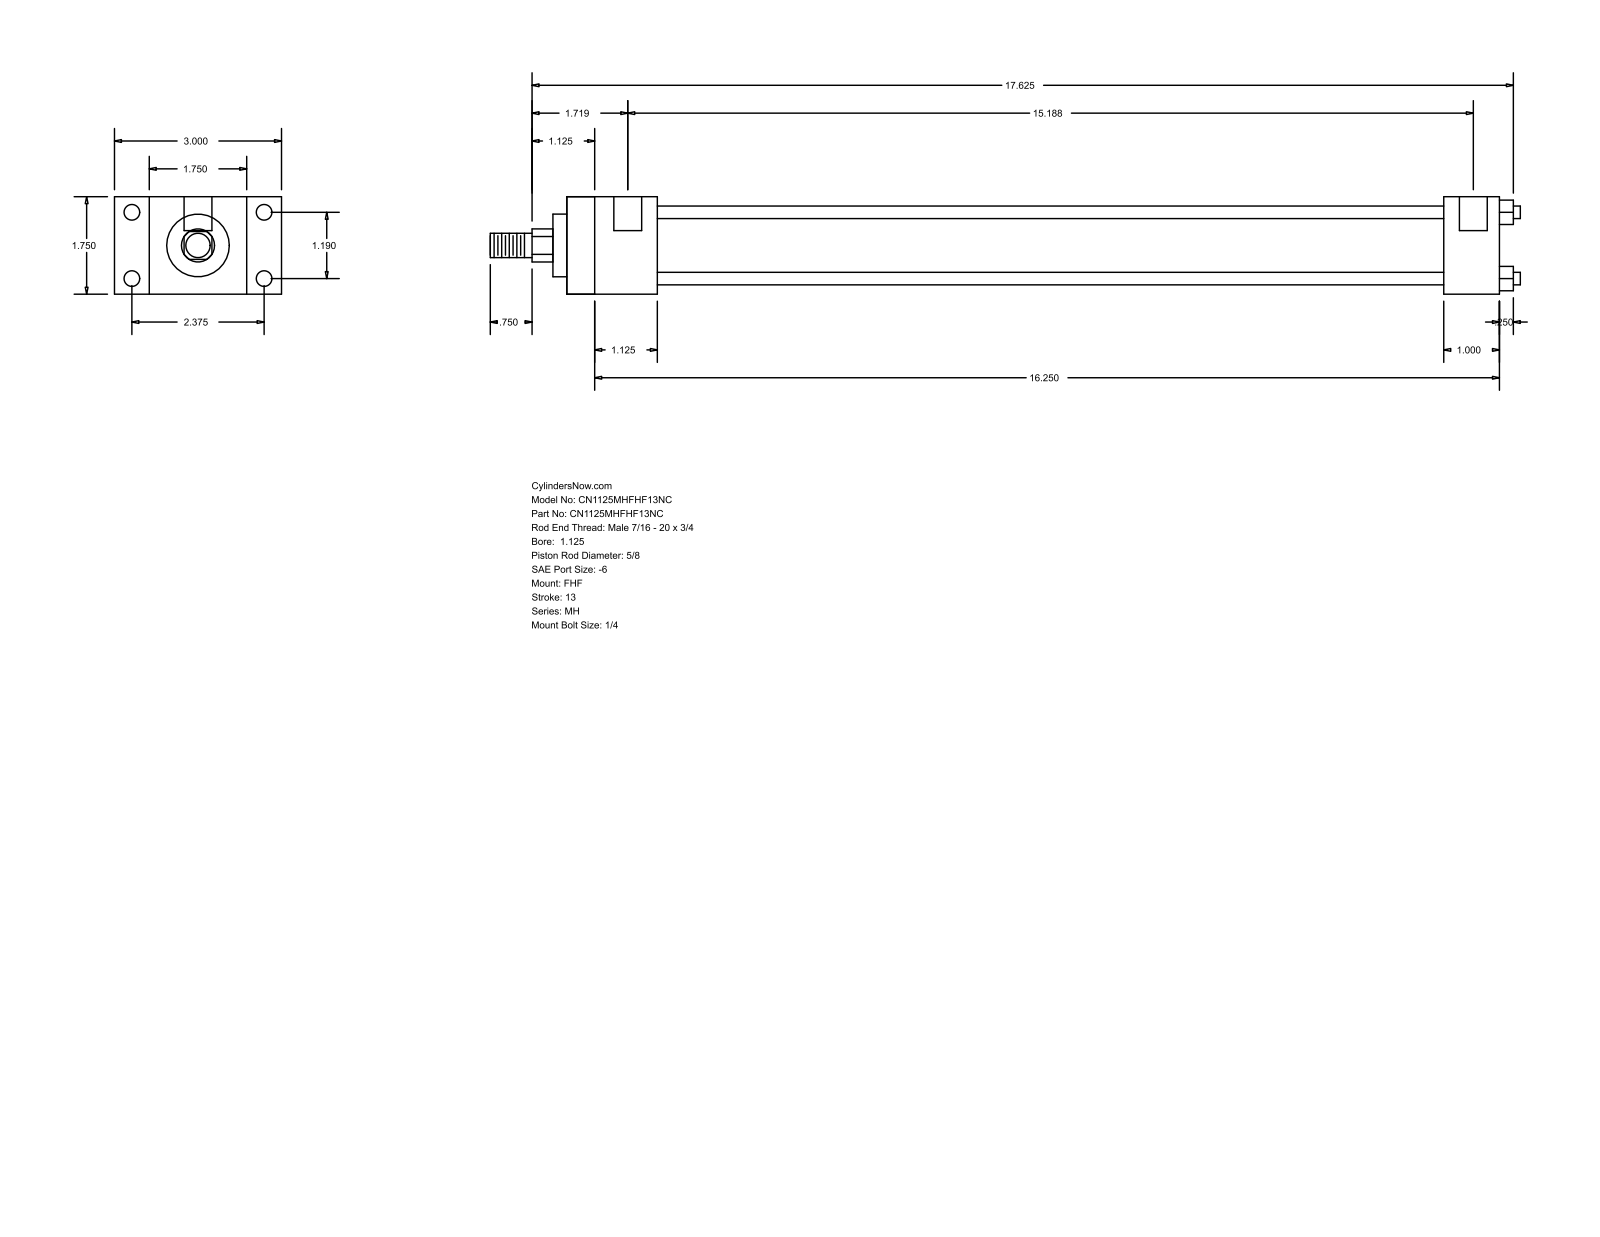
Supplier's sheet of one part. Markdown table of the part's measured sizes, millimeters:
| quantity | value |
| --- | --- |
| part name | MH_FHF__0112_0.625 |
| STEP written by | GSSL Pune (CONFIG_CONTROL_DESIGN) |
| units | millimeters |
| bodies | 0 solids, 88 faces (60 planar, 28 cylindrical, 0 other) |
| overall size | 469.9 × 76.2 × 44.45 |
| round holes (diameter × count) | 5.56 × 4, 7.14 × 4, 12.7 × 2 |
| round bosses / shafts (diameter × count) | 5.71 × 4, 34.92 × 1, 28.57 × 1, 15.88 × 1, 11.11 × 1 |
| partial cylindrical surfaces (radius × count) | 7.54 × 1 |
| main face-to-face distances | 44.46, 15.87, 60.33, 41.27, 76.2, 425.44, 384.17, 400.05, 358.78, 25.39 |
| hole center spacings | 30.22, 60.32, 67.47, 382.59, 3.17, 385.76 |
